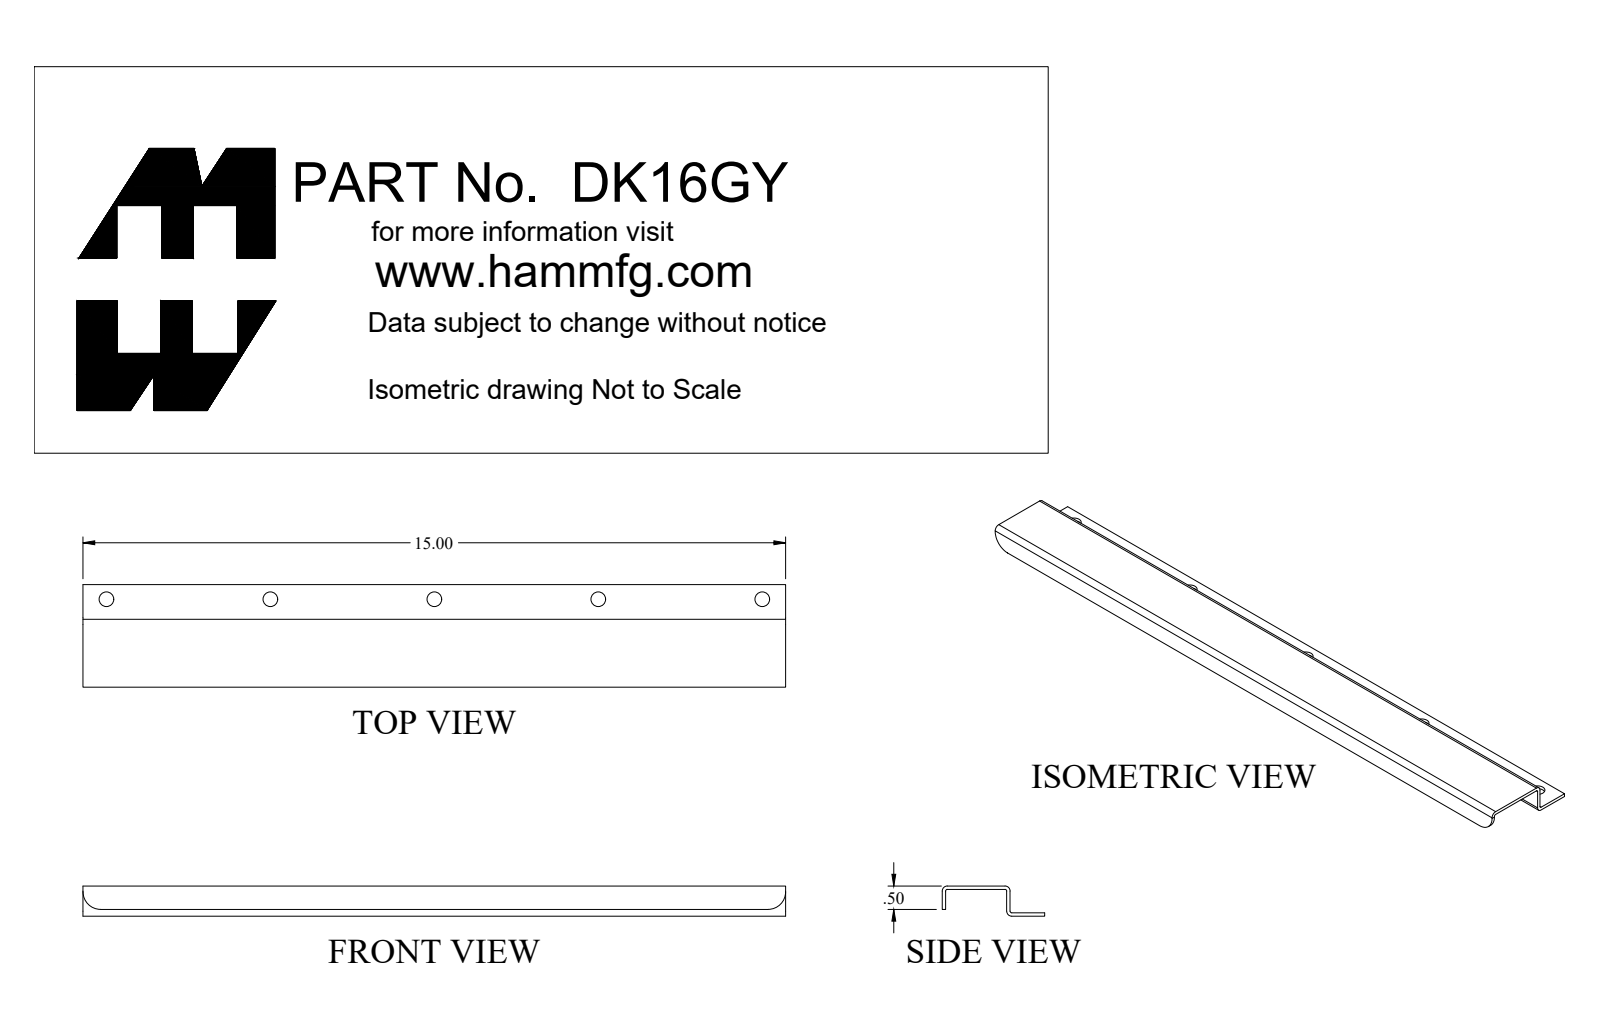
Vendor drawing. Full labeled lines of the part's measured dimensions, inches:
Part name (STEP PRODUCT): DK16GY_Default
STEP written by: SolidWorks 2018 (CONFIG_CONTROL_DESIGN)
Units: inches
Bodies: 5 solids, 69 faces (35 planar, 28 cylindrical, 6 other)
Overall size (bounding box): 15 × 2.188 × 1.322
Volume: 4.131 in³ · Surface area: 122.1 in²
Round holes (diameter × count): ⌀0.313 ×5, ⌀0.201 ×1, ⌀0.275 ×1
Round bosses / shafts (diameter × count): ⌀0.625 ×1, ⌀0.483 ×1, ⌀0.25 ×1
Partial cylindrical surfaces — rounded edges, fillets, slot ends (radius × count): R0.036 ×3, R0.108 ×3, R0.375 ×2
Main face-to-face distances: 0.072, 0.572, 0.644, 1.376, 0.5, 0.063, 0.635, 0.707, 0.135, 1.448
Hole centre spacings: 3.5, 7, 10.5, 14
